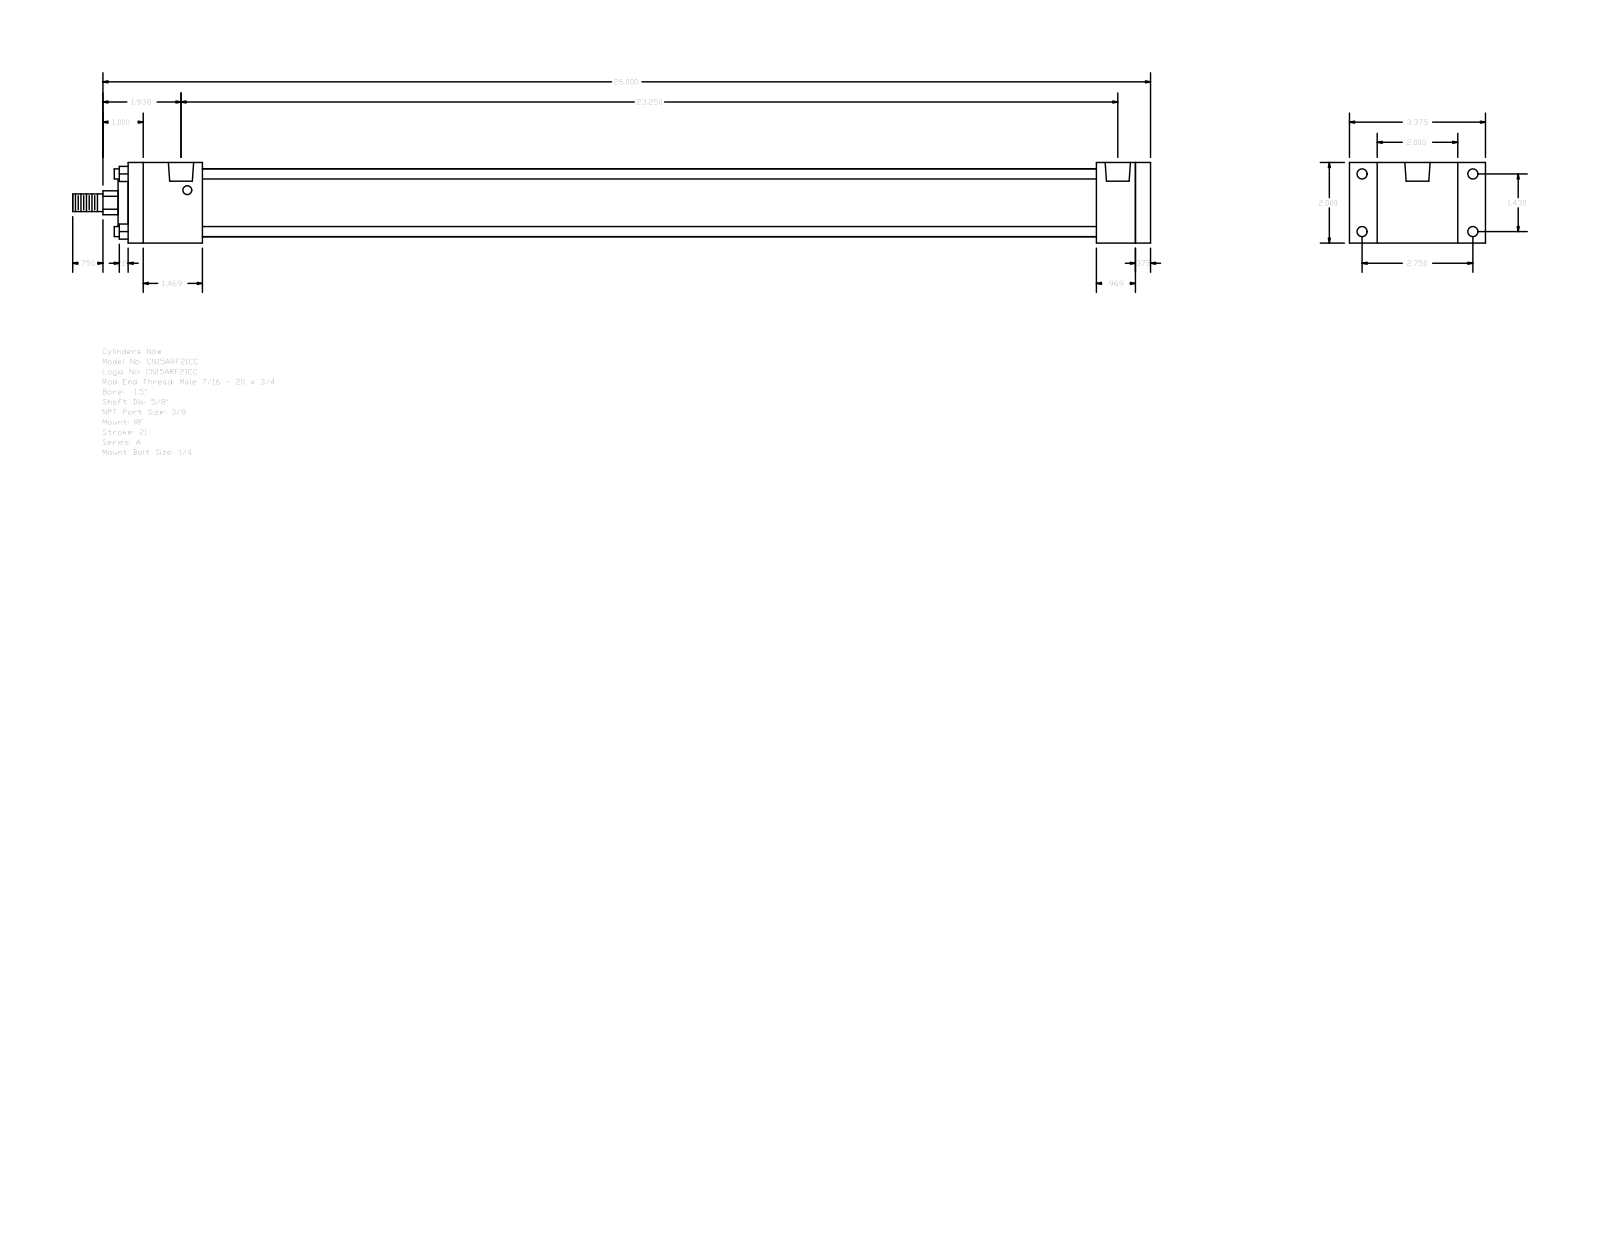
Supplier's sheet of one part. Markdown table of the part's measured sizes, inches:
| quantity | value |
| --- | --- |
| part name | A_RF__0150_0.625 |
| STEP written by | GSSL Pune (CONFIG_CONTROL_DESIGN) |
| units | inches |
| bodies | 0 solids, 92 faces (64 planar, 28 cylindrical, 0 other) |
| overall size | 26.75 × 3.375 × 2 |
| round holes (diameter × count) | 0.219 × 4, 0.25 × 4, 0.627 × 2 |
| round bosses / shafts (diameter × count) | 0.25 × 4, 1.69 × 1, 1.125 × 1, 0.625 × 1, 0.437 × 1 |
| partial cylindrical surfaces (radius × count) | 0.297 × 1 |
| main face-to-face distances | 2, 0.375, 25, 25.375, 24.031, 0.969, 1.344, 1.844, 22.187, 23.156 |
| hole center spacings | 0.156, 1.43, 2.75, 3.099, 22.937, 23.094, 23.25 |
